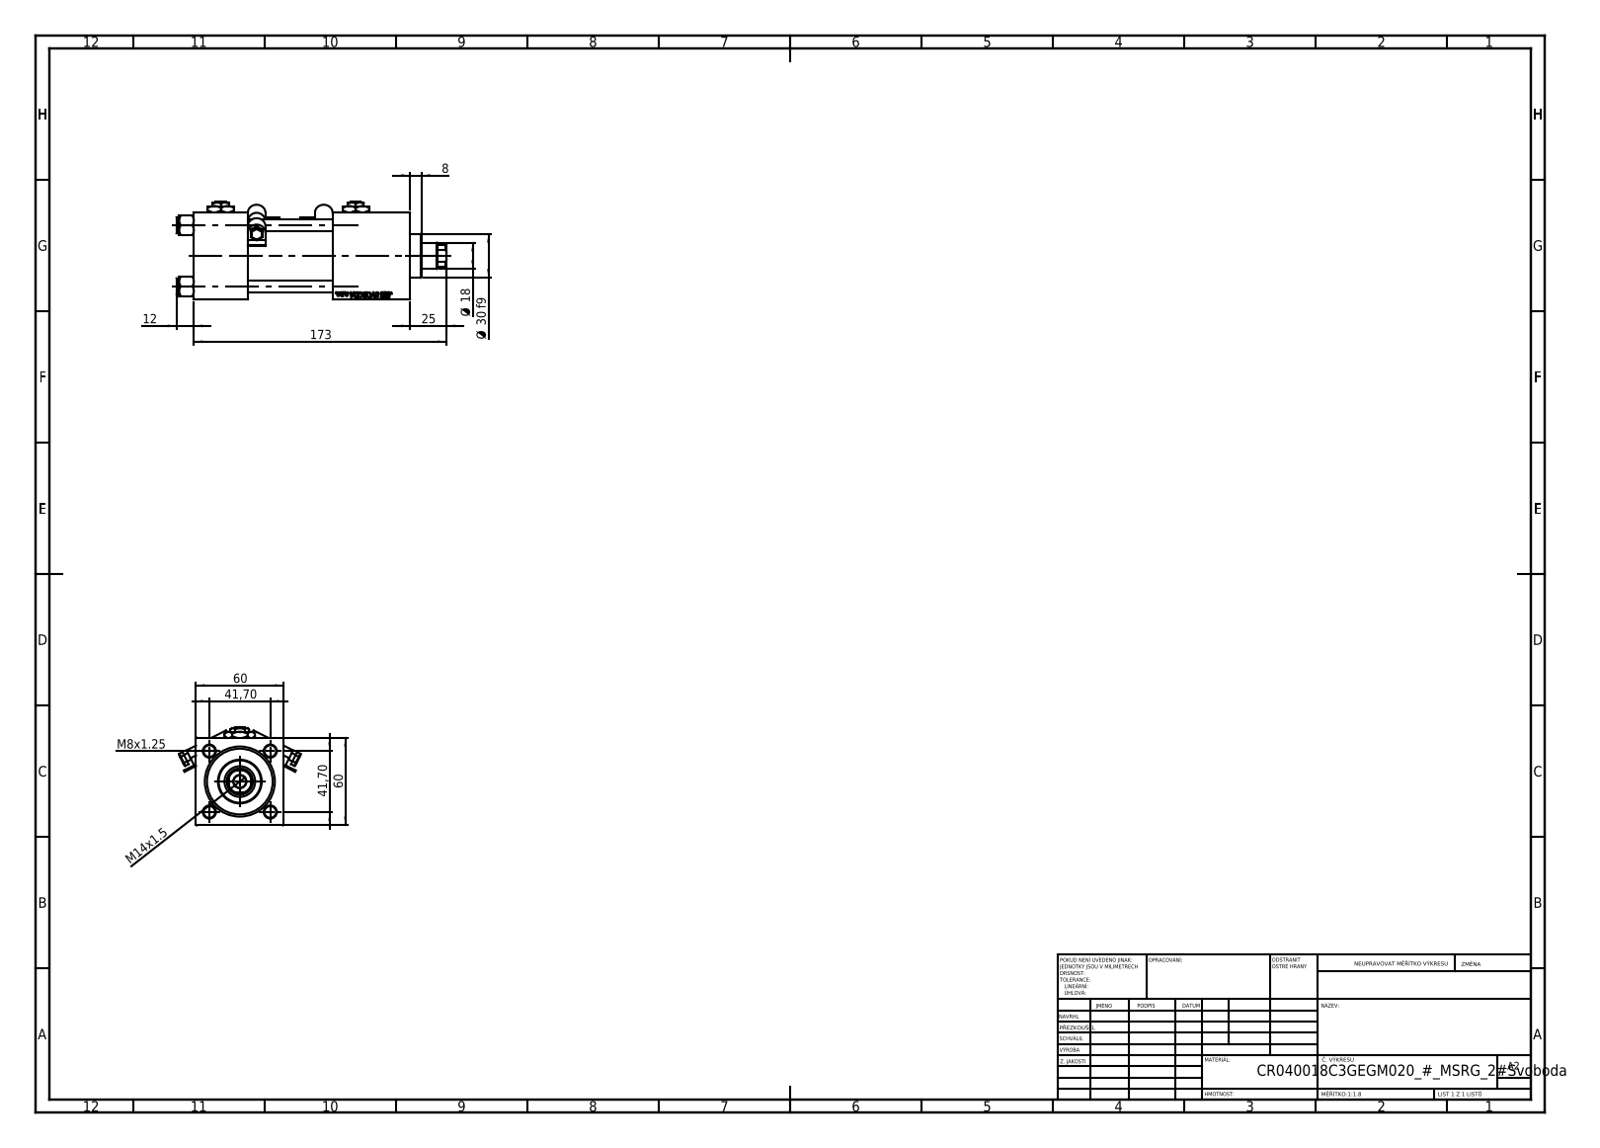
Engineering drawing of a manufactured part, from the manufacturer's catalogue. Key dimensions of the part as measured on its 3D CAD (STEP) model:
Part name (STEP PRODUCT): Zatka_pro_OIL_PORT; MSRF_MSRG1; V215CR_VCP_C; V215CR_C_Body (+3 more)
STEP written by: SolidWorks 2019 (CONFIG_CONTROL_DESIGN)
Units: millimetres
Bodies: 15 solids, 1314 faces (610 planar, 126 cylindrical, 578 other)
Overall size (bounding box): 185 × 83.44 × 67
Volume: 405 915 mm³ · Surface area: 112 628 mm²
Round holes (diameter × count): ⌀8 ×4, ⌀7 ×2, ⌀16.66 ×2, ⌀24 ×2, ⌀8.5 ×1, ⌀18 ×1, ⌀21 ×1, ⌀31 ×1, ⌀40 ×1, ⌀45 ×1
Round bosses / shafts (diameter × count): ⌀11 ×4, ⌀5 ×2, ⌀2.5 ×2, ⌀46 ×1, ⌀30 ×1
Partial cylindrical surfaces — rounded edges, fillets, slot ends (radius × count): R0.5 ×12, R6 ×4, R8.5 ×1
Main face-to-face distances: 60, 37, 53, 95, 58, 148, 111, 119.3, 82.3, 24.3
Hole centre spacings: 29.49, 41.7, 58.97, 92.5
